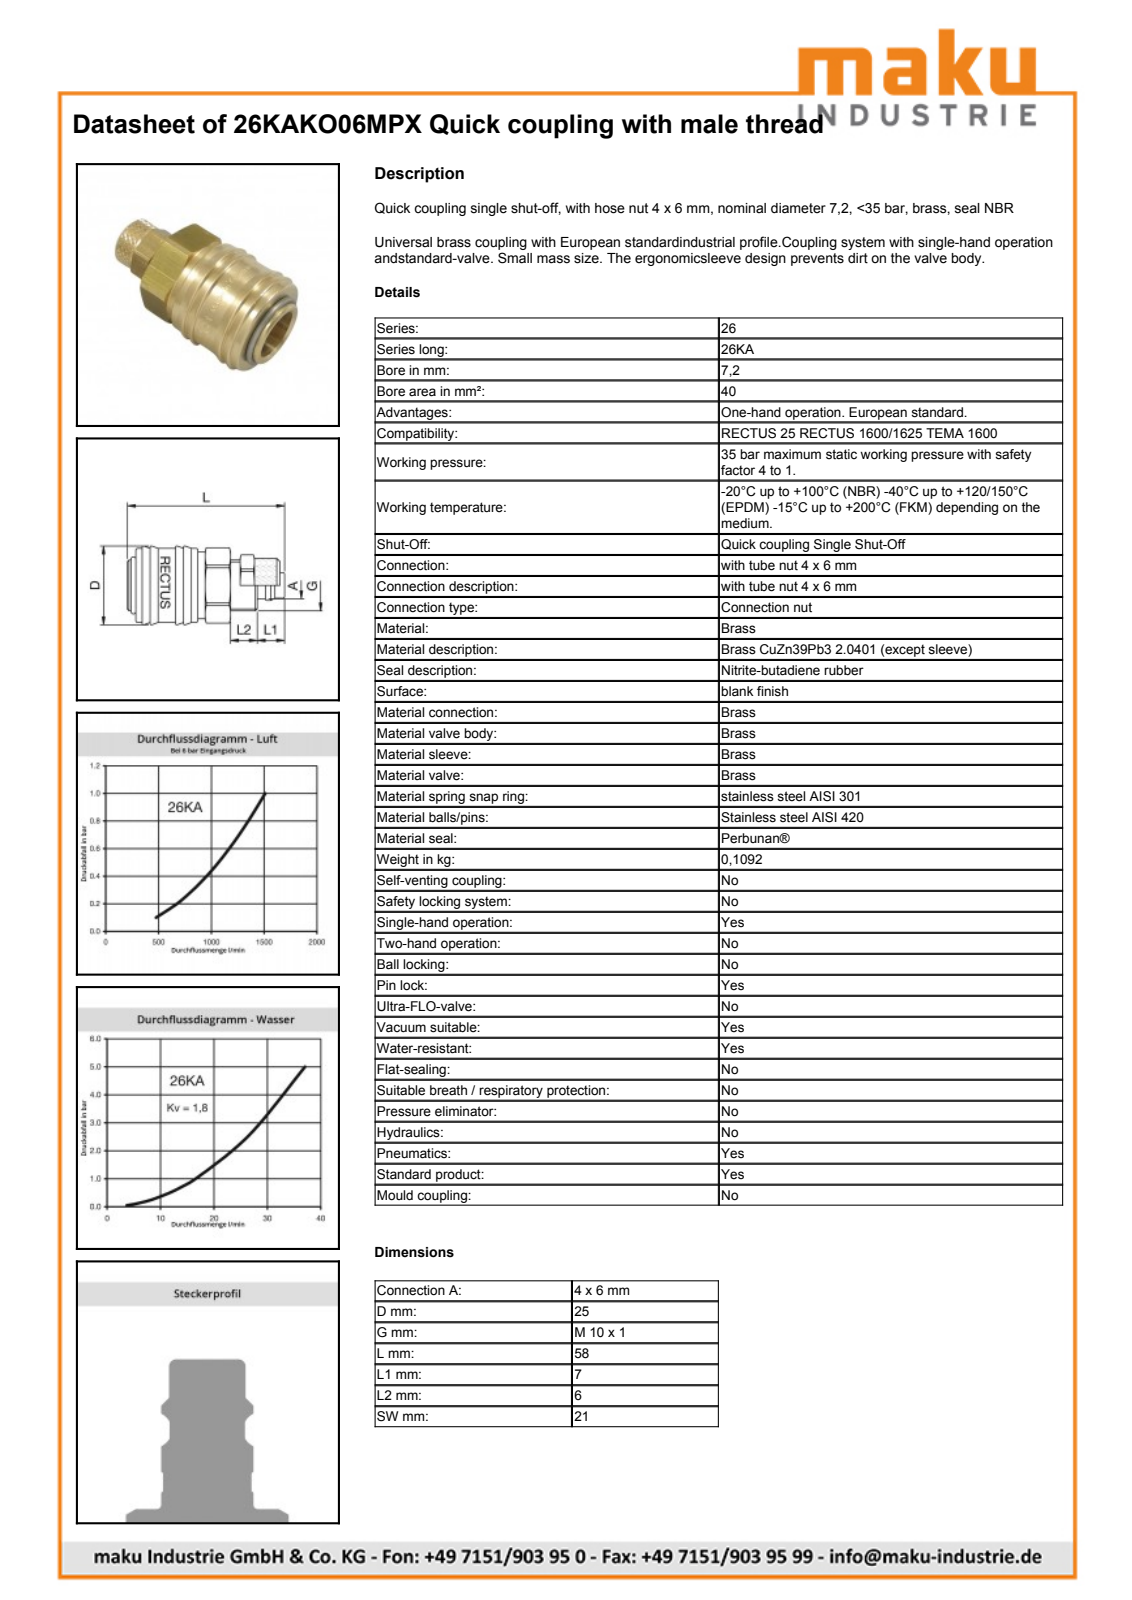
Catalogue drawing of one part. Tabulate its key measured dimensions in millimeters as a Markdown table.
| quantity | value |
| --- | --- |
| part name | D105135 |
| STEP written by | Autodesk Inventor 2011 (AUTOMOTIVE_DESIGN) |
| units | millimeters |
| bodies | 2 solids, 583 faces (236 planar, 80 cylindrical, 267 other) |
| overall size | 45.33 × 24.8 × 24.8 |
| volume | 7 770 mm³ |
| surface area | 7 503 mm² |
| round holes (diameter × count) | 6.2 × 1, 9.45 × 1, 17 × 1, 23.3 × 1 |
| round bosses / shafts (diameter × count) | 21.1 × 1, 21 × 1, 18 × 1, 16.65 × 1, 16.1 × 1, 15.95 × 1, 14.95 × 1, 12 × 1 |
| partial cylindrical surfaces (radius × count) | 6.75 × 1, 7.85 × 1, 11.55 × 1, 11.85 × 1 |
| main face-to-face distances | 21, 29.5, 2.65, 32.15, 18.35, 11.15, 12, 1.15, 45.33, 42.68 |
